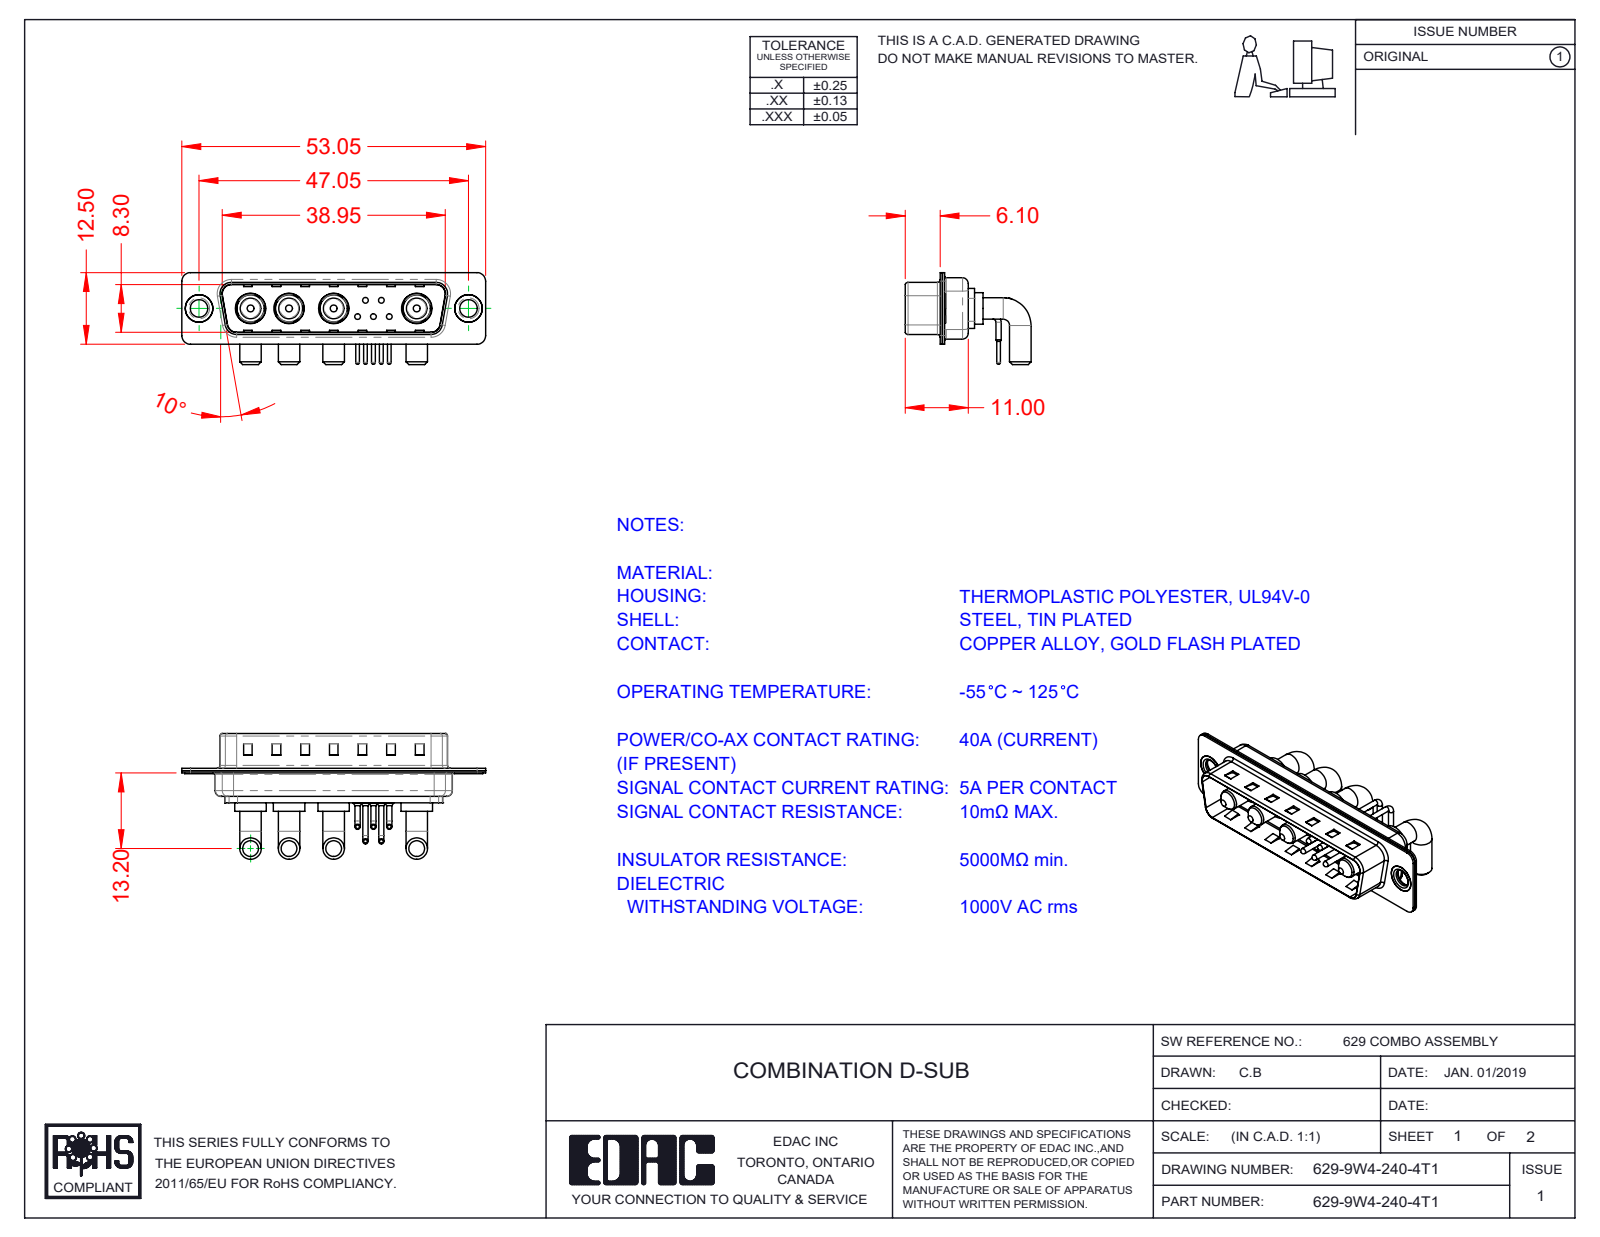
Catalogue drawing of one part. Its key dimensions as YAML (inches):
part_name: "629Combo Contact Row 2; 629Combo Housing_9W4; 629Combo Shell Front_25 Contacts; 629-9W4-240-4T1 (+4 more)"
step_written_by: "SolidWorks 2020 (CONFIG_CONTROL_DESIGN)"
units: inches
bodies: {solids: 18, faces: 1072, planar: 531, cylindrical: 385, other: 156}
overall_size: [2.089, 0.865, 0.632]
volume: 0.215
surface_area: 11.29
round_holes:
  - {diameter: 0.03, count: 5}
  - {diameter: 0.063, count: 5}
  - {diameter: 0.079, count: 5}
  - {diameter: 0.191, count: 4}
  - {diameter: 0.209, count: 4}
  - {diameter: 0.12, count: 2}
  - {diameter: 0.157, count: 2}
  - {diameter: 0.189, count: 2}
round_bosses_or_shafts:
  - {diameter: 0.035, count: 10}
  - {diameter: 0.148, count: 8}
  - {diameter: 0.059, count: 5}
  - {diameter: 0.039, count: 5}
  - {diameter: 0.026, count: 5}
  - {diameter: 0.217, count: 4}
  - {diameter: 0.205, count: 4}
  - {diameter: 0.187, count: 4}
partial_cylinders:
  - {radius: 0.059, count: 16}
  - {radius: 0.079, count: 12}
  - {radius: 0.02, count: 8}
  - {radius: 0.063, count: 8}
  - {radius: 0.04, count: 5}
  - {radius: 0.01, count: 4}
  - {radius: 0.024, count: 4}
  - {radius: 0.026, count: 4}
face_to_face_distances: [0.016, 0.031, 0.374, 0.358, 0.343, 0.39, 0.03, 0.047, 0.22, 0.014]
hole_center_spacings: [0.124, 0.109, 0.198, 0.571, 0.109, 0.173, 0.174, 0.197]
